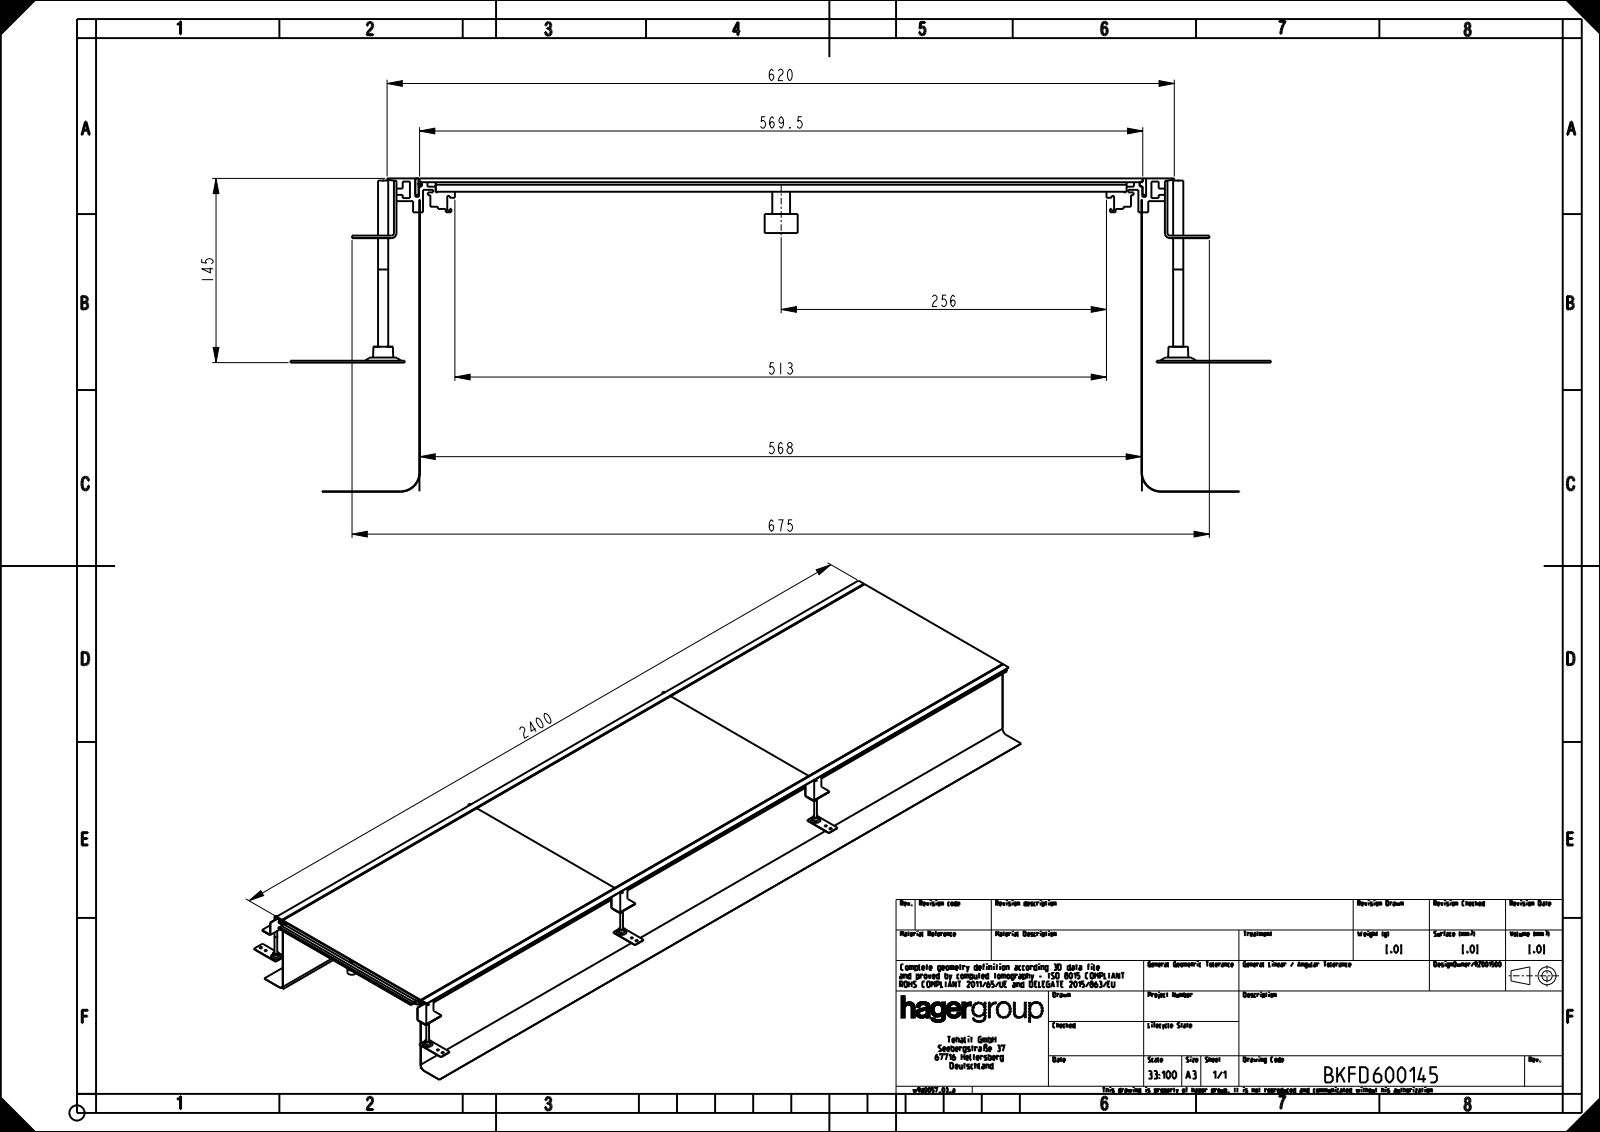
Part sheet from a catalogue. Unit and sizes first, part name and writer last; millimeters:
Units: millimetres
Overall size (bounding box): 2432.5 × 772.13 × 246.7
Round holes (diameter × count): ⌀7 ×15, ⌀8 ×9, ⌀10 ×9, ⌀6 ×6, ⌀8.5 ×6, ⌀11.5 ×6, ⌀17.5 ×6, ⌀23 ×6
Round bosses / shafts (diameter × count): ⌀26 ×9, ⌀14 ×9, ⌀11.9 ×9, ⌀20 ×6, ⌀8 ×6
Partial cylindrical surfaces — rounded edges, fillets, slot ends (radius × count): R2 ×92, R3 ×24, R0.5 ×20, R4 ×2, R15 ×2, R15.4 ×2
Main face-to-face distances: 3, 0.4, 568.55, 568.95, 568.15, 243.7, 246.7, 243.3, 246.3, 7.5
Hole centre spacings: 800, 1600, 800.25, 801.1, 802.4, 1042.3, 1055.24, 1083.09
Volume: 9 248 000 mm³ · Surface area: 8 166 000 mm²
Bodies: 62 solids, 1026 faces (600 planar, 354 cylindrical, 72 other)
Part name (STEP PRODUCT): U05644KUN; U05650KUN; U05647KUN; U05826KUN (+8 more)
STEP written by: CREO PARAMETRIC BY PTC INC, 2020281 (AUTOMOTIVE_DESIGN)
